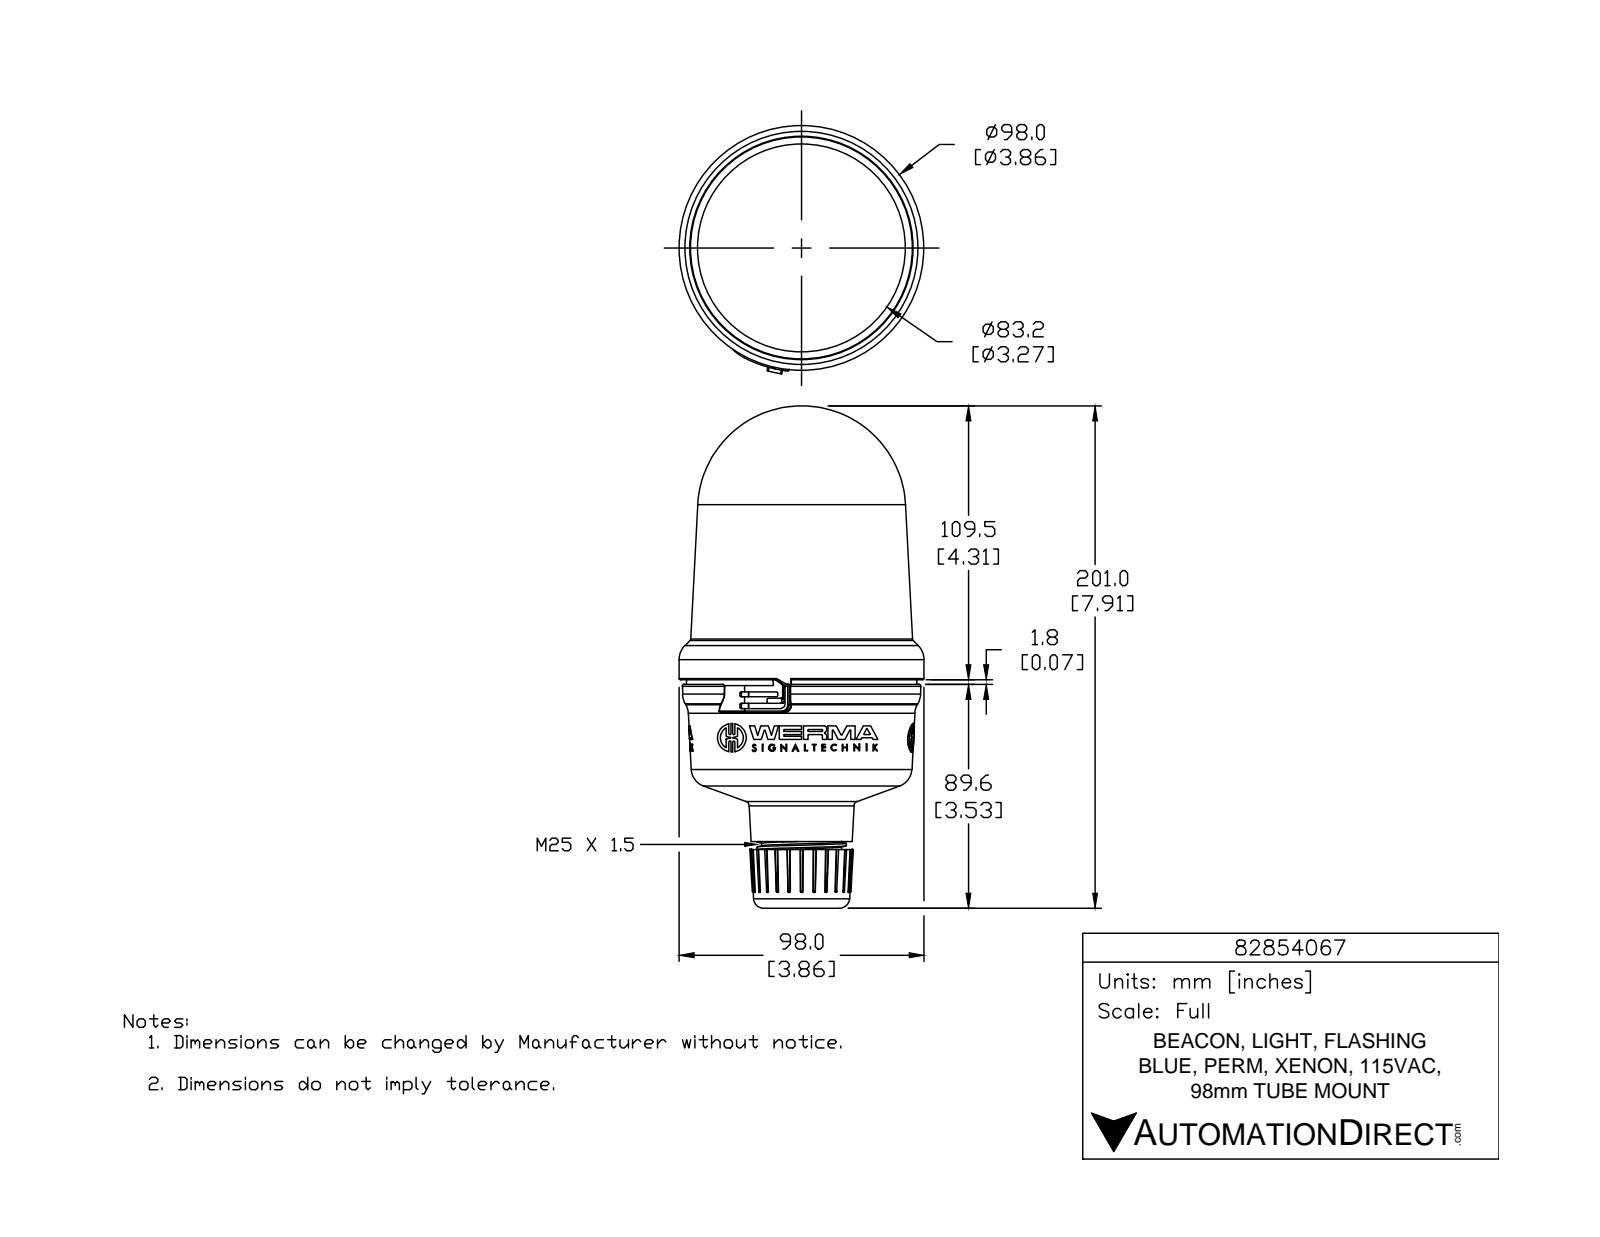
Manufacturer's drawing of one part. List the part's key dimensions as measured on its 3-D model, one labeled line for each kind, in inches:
Part name (STEP PRODUCT): 82854067
STEP written by: SolidWorks 2015 (AUTOMOTIVE_DESIGN)
Units: inches
Bodies: 1 solid, 1006 faces (554 planar, 189 cylindrical, 263 other)
Overall size (bounding box): 7.914 × 3.912 × 3.858
Volume: 54.7 in³ · Surface area: 91.39 in²
Round holes (diameter × count): ⌀0.078 ×3, ⌀1.013 ×1, ⌀1.024 ×1
Round bosses / shafts (diameter × count): ⌀0.452 ×3, ⌀0.113 ×3, ⌀3.858 ×1, ⌀1.409 ×1, ⌀1.261 ×1
Partial cylindrical surfaces — rounded edges, fillets, slot ends (radius × count): R0.02 ×12, R0.007 ×9, R0.007 ×6, R0.016 ×6, R0.016 ×6, R0.016 ×6, R0.262 ×6, R0.006 ×3
Main face-to-face distances: 2.214, 0.462, 2.676, 0.335, 0.127, 2.548, 2.603, 2.476, 2.141, 0.073
